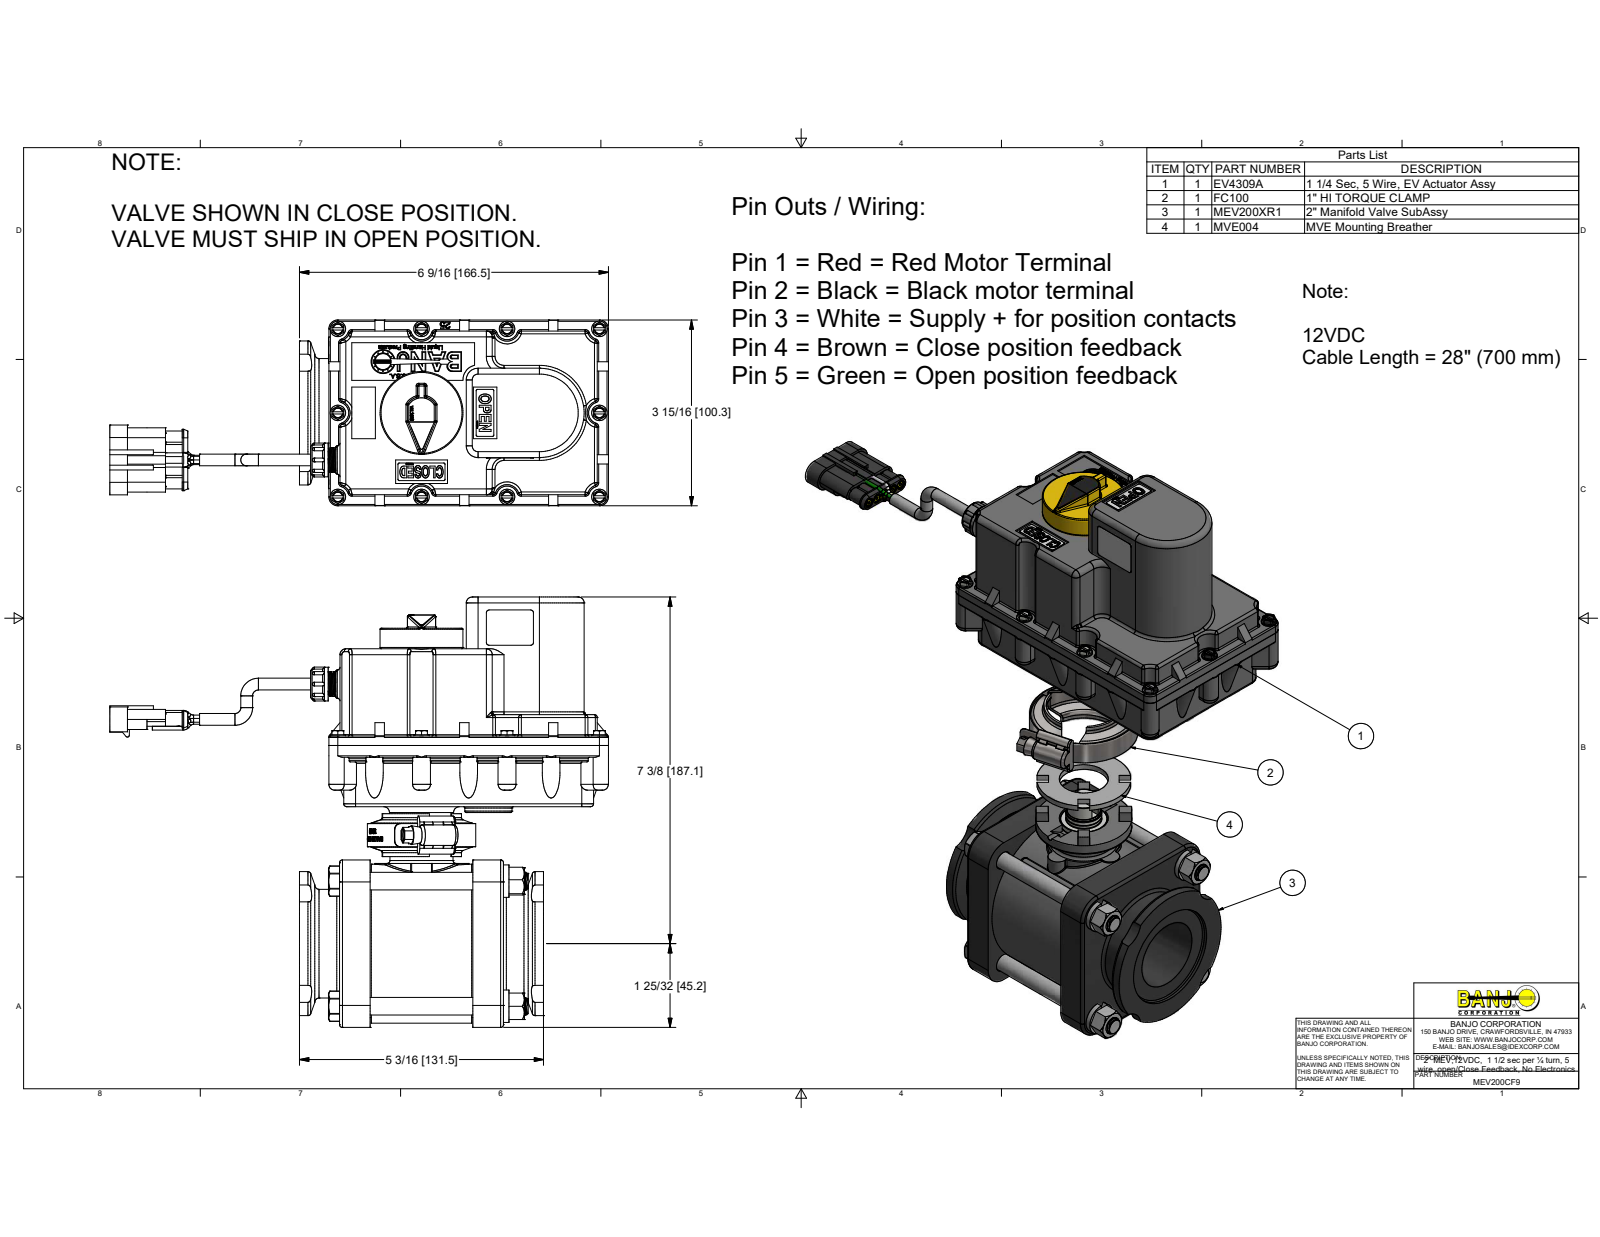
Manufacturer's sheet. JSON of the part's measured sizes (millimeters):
{"part_name": "MEV20254AX; MEV20254A; VE20255SSH; MEV10151SS (+8 more)", "step_written_by": "Autodesk Inventor 2014 (AUTOMOTIVE_DESIGN)", "units": "millimeters", "bodies": {"solids": 74, "faces": 6586, "planar": 2622, "cylindrical": 1755, "other": 2209}, "overall_size": [300.92, 232.31, 100.33], "volume_mm3": 1222000, "surface_area_mm2": 441670, "round_holes": [[2.79, 10], [4.06, 10], [5.08, 10], [3.05, 6], [3.81, 6], [1.4, 5], [5.5, 5], [4.47, 4], [7.81, 4], [9.78, 4], [10.31, 4], [9.52, 3]], "round_bosses_or_shafts": [[8.24, 60], [2.03, 19], [8.33, 10], [3.51, 10], [2.62, 8], [8, 6], [7.62, 6], [17.46, 5]], "partial_cylinders_radius": [[0.76, 121], [0.51, 71], [1.52, 55], [3.17, 28], [8, 24], [12.7, 24], [0.5, 21], [0.18, 20]], "face_to_face_distances": [3.18, 21.59, 1.9, 85.22, 5.08, 27.94, 6.98, 33.02, 38.1, 82.04], "hole_center_spacings": [42.68, 52.25, 52.27, 60.34, 60.36, 33.76, 45.34, 6]}
